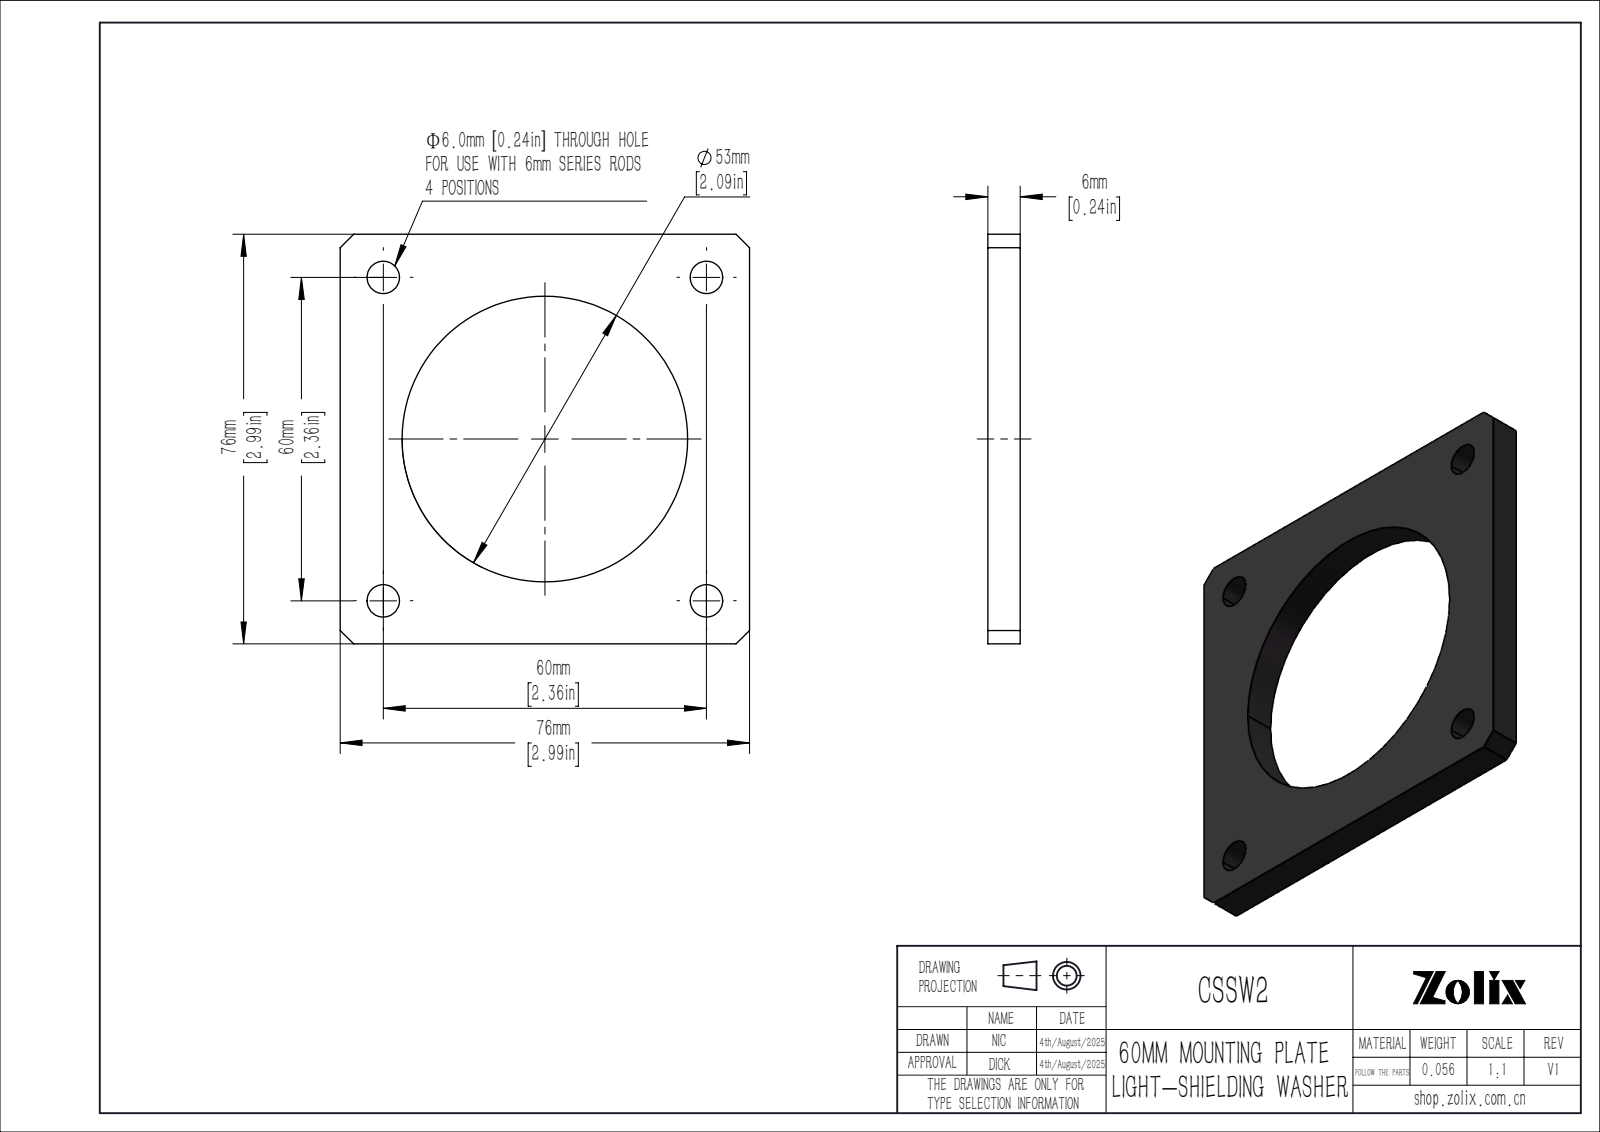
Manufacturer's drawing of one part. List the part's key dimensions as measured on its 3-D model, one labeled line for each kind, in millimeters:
Part name (STEP PRODUCT): CSSW2
STEP written by: SolidWorks 2020 (CONFIG_CONTROL_DESIGN)
Units: millimetres
Bodies: 1 solid, 20 faces (10 planar, 10 cylindrical, 0 other)
Overall size (bounding box): 76 × 76 × 6
Volume: 20 661 mm³ · Surface area: 10 129 mm²
Round holes (diameter × count): ⌀6.02 ×4, ⌀53 ×1
Main face-to-face distances: 6, 76, 103.93, 103.92
Hole centre spacings: 42.43, 60, 84.85
